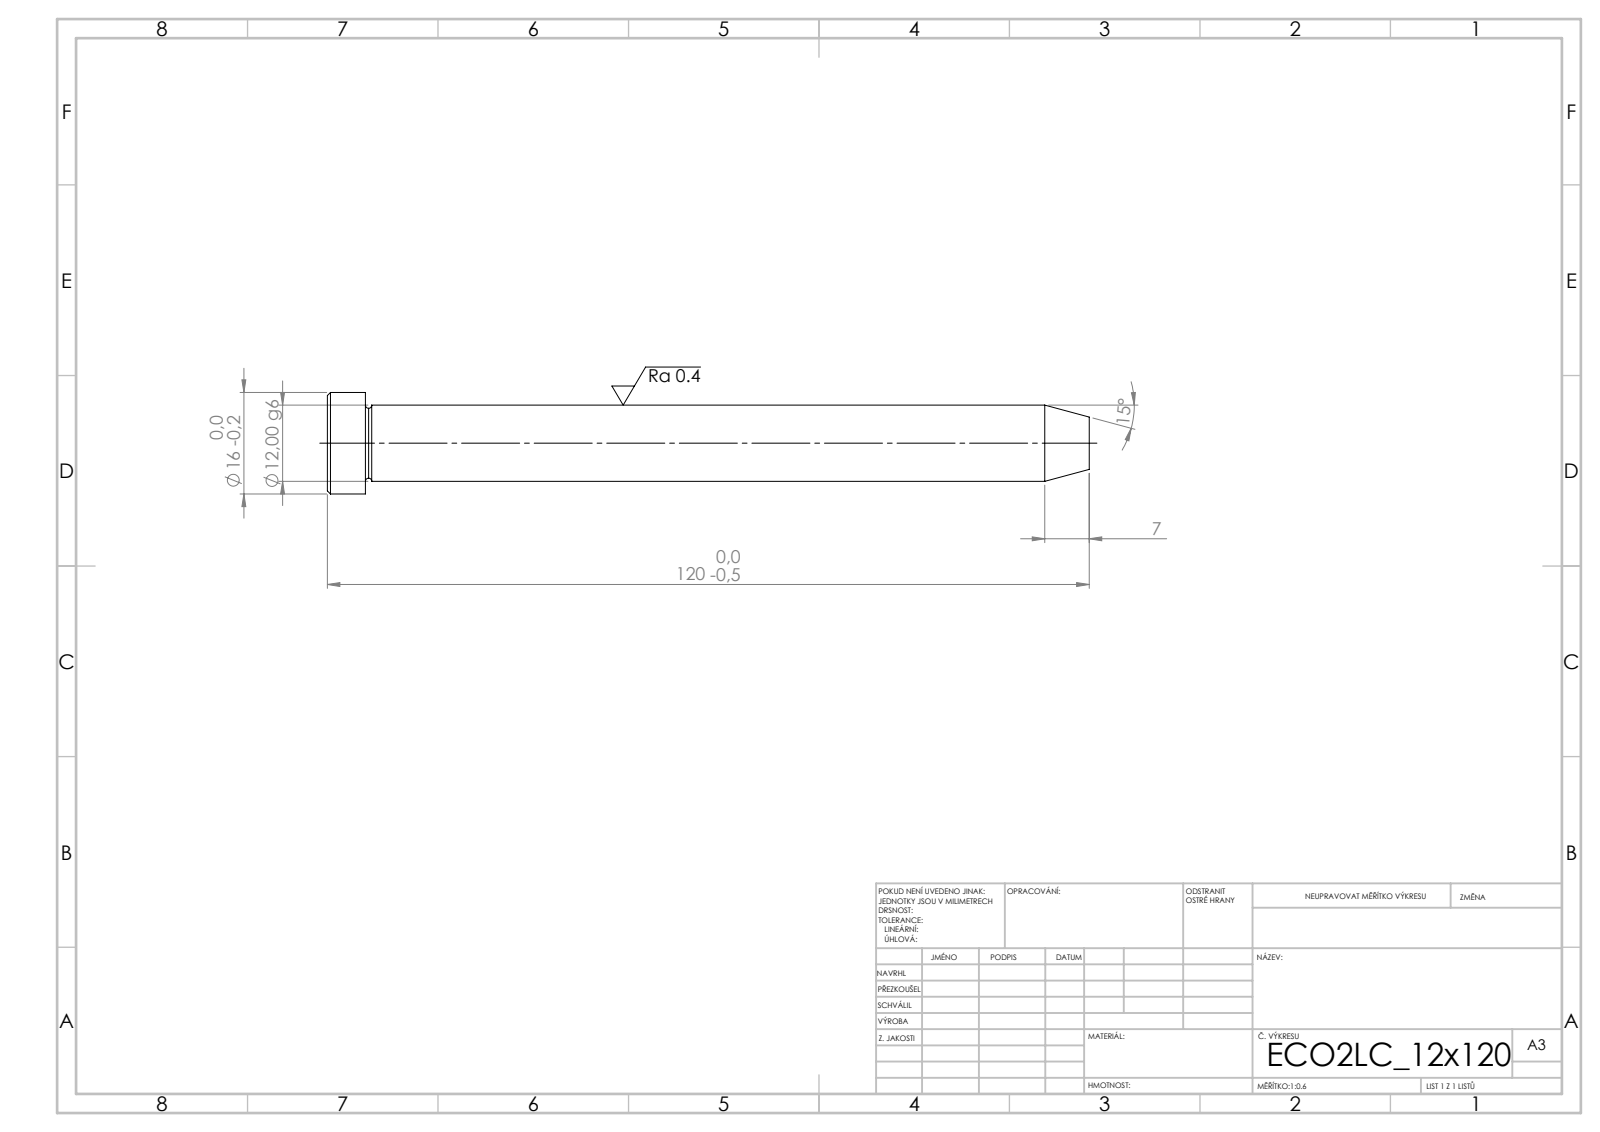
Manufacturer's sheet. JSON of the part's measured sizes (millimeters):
{"step_written_by": "SolidWorks 2019 (CONFIG_CONTROL_DESIGN)", "units": "millimeters", "bodies": {"solids": 1, "faces": 15, "planar": 3, "cylindrical": 4, "other": 8}, "overall_size": [120, 16, 16], "volume_mm3": 13857, "surface_area_mm2": 4912, "round_bosses_or_shafts": [[16, 1], [12, 1]], "face_to_face_distances": [6, 114, 120]}
